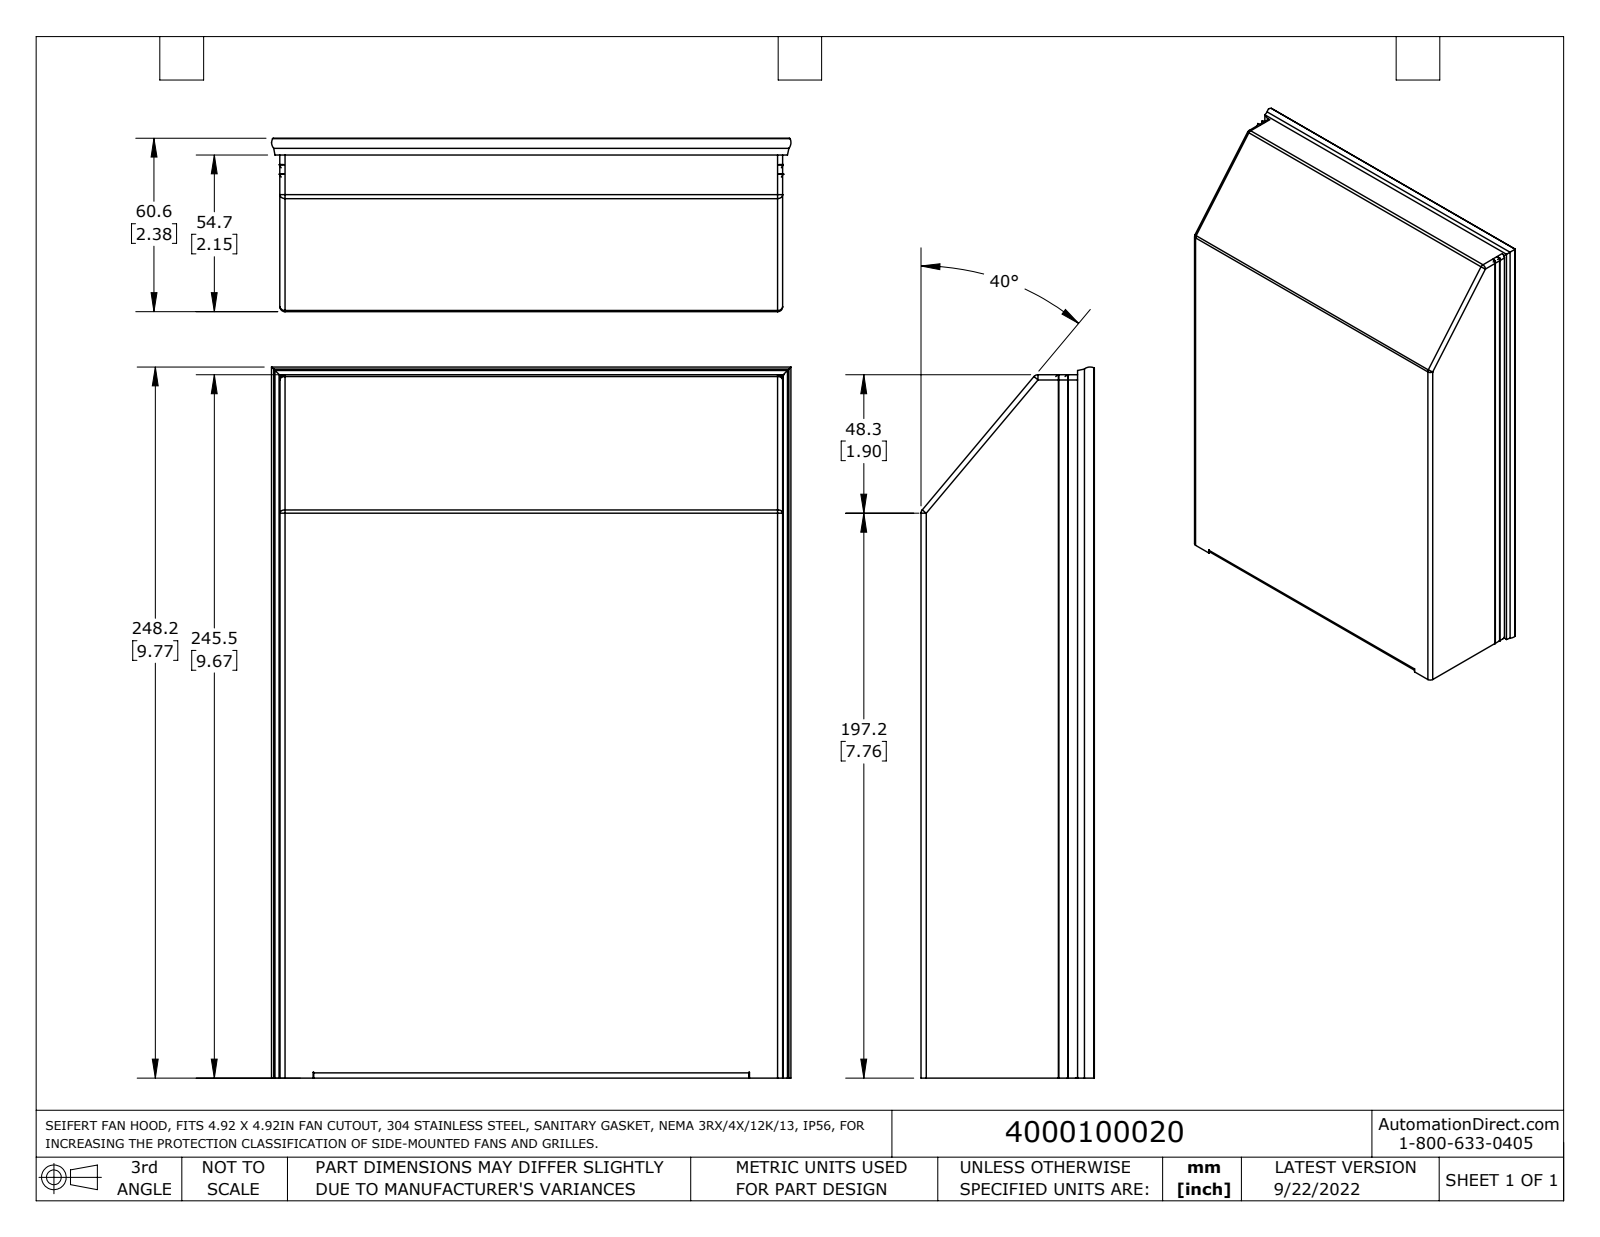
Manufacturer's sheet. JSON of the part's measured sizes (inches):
{"part_name": "fc4000_100", "step_written_by": "SolidWorks 2021 (AUTOMOTIVE_DESIGN)", "units": "inches", "bodies": {"solids": 11, "faces": 439, "planar": 199, "cylindrical": 202, "other": 38}, "overall_size": [9.772, 7.142, 2.384], "volume_in3": 9.219, "surface_area_in2": 427.9, "round_holes": [[0.217, 4], [0.134, 2], [0.197, 2]], "round_bosses_or_shafts": [[0.236, 2]], "partial_cylinders_radius": [[0.118, 23], [0.039, 21], [0.071, 14], [0.004, 12], [0.278, 12], [1.181, 12], [0.008, 9], [0.059, 6]], "face_to_face_distances": [0.031, 6.85, 6.882, 0.059, 0.228, 0.197, 6.913, 6.535, 0.378, 0.319], "hole_center_spacings": [4.409, 7.717, 8.887, 5.709]}
